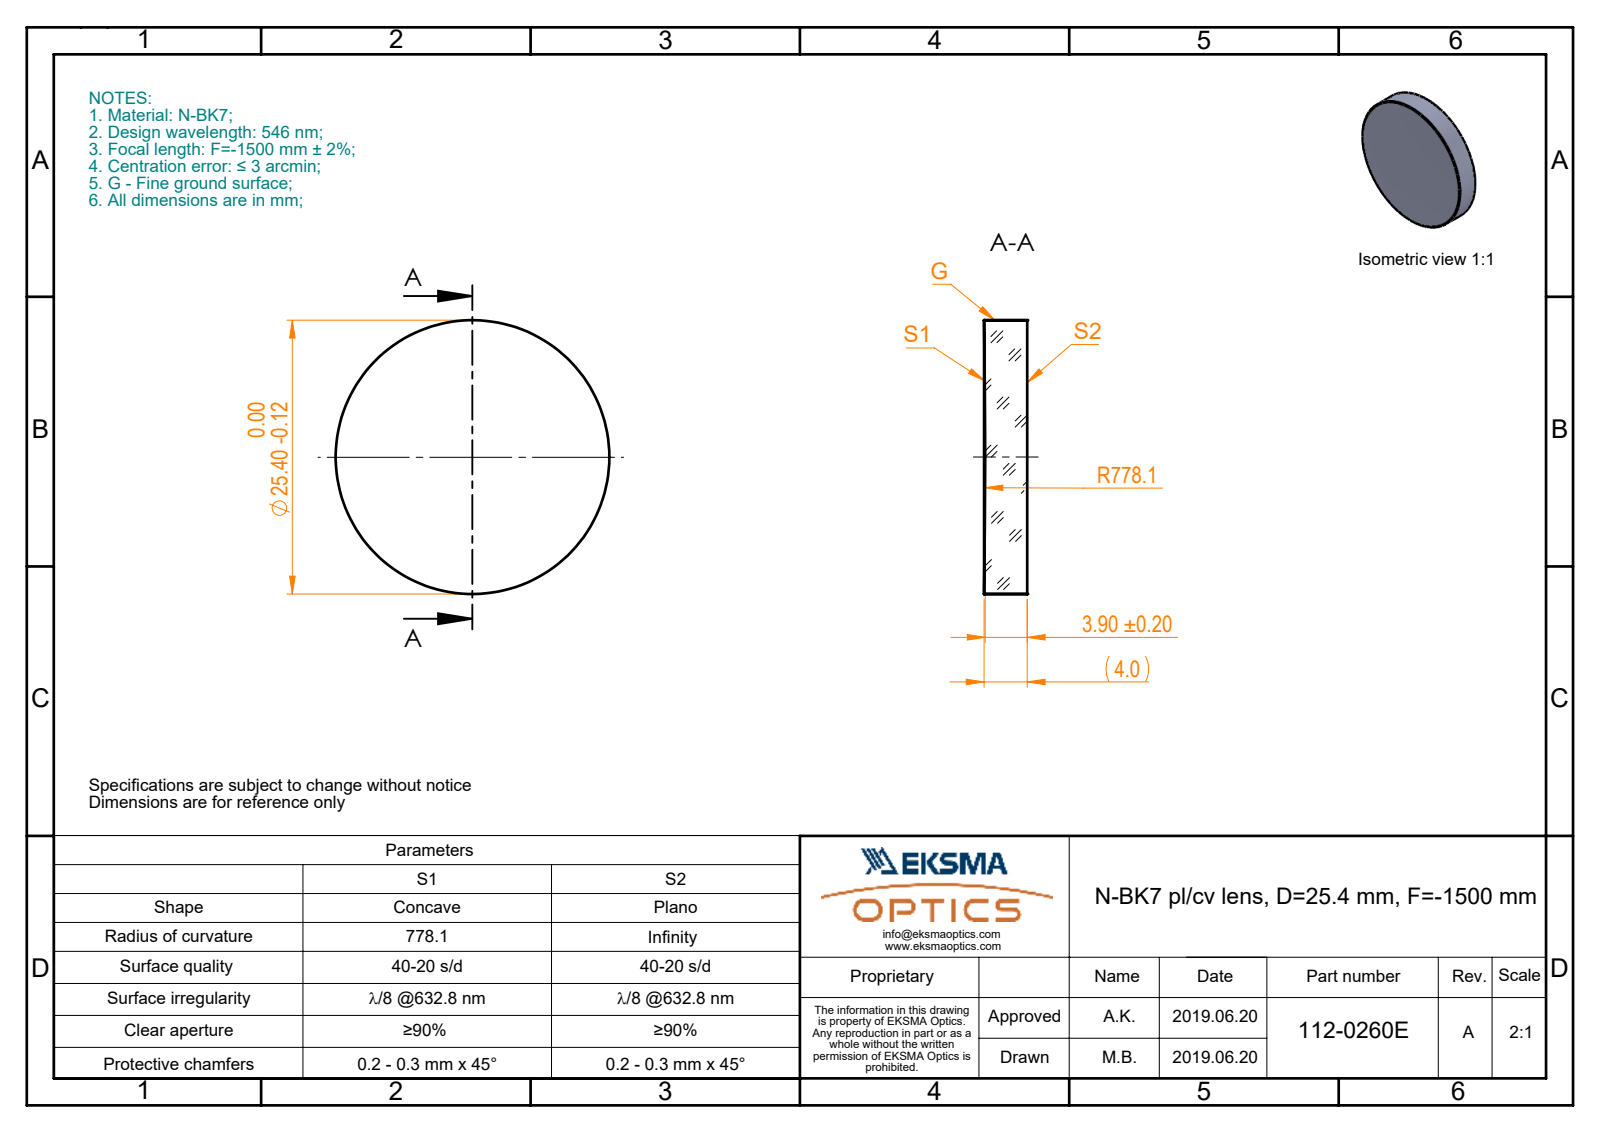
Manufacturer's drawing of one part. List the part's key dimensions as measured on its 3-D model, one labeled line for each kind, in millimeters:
Part name (STEP PRODUCT): 112-0260E BK7 pl-cv 25.4 F-1500
STEP written by: SolidWorks 2017 (CONFIG_CONTROL_DESIGN)
Units: millimetres
Bodies: 1 solid, 5 faces (1 planar, 2 cylindrical, 2 other)
Overall size (bounding box): 25.4 × 25.4 × 4
Volume: 2 002 mm³ · Surface area: 1 333 mm²
Round bosses / shafts (diameter × count): ⌀25.4 ×1
